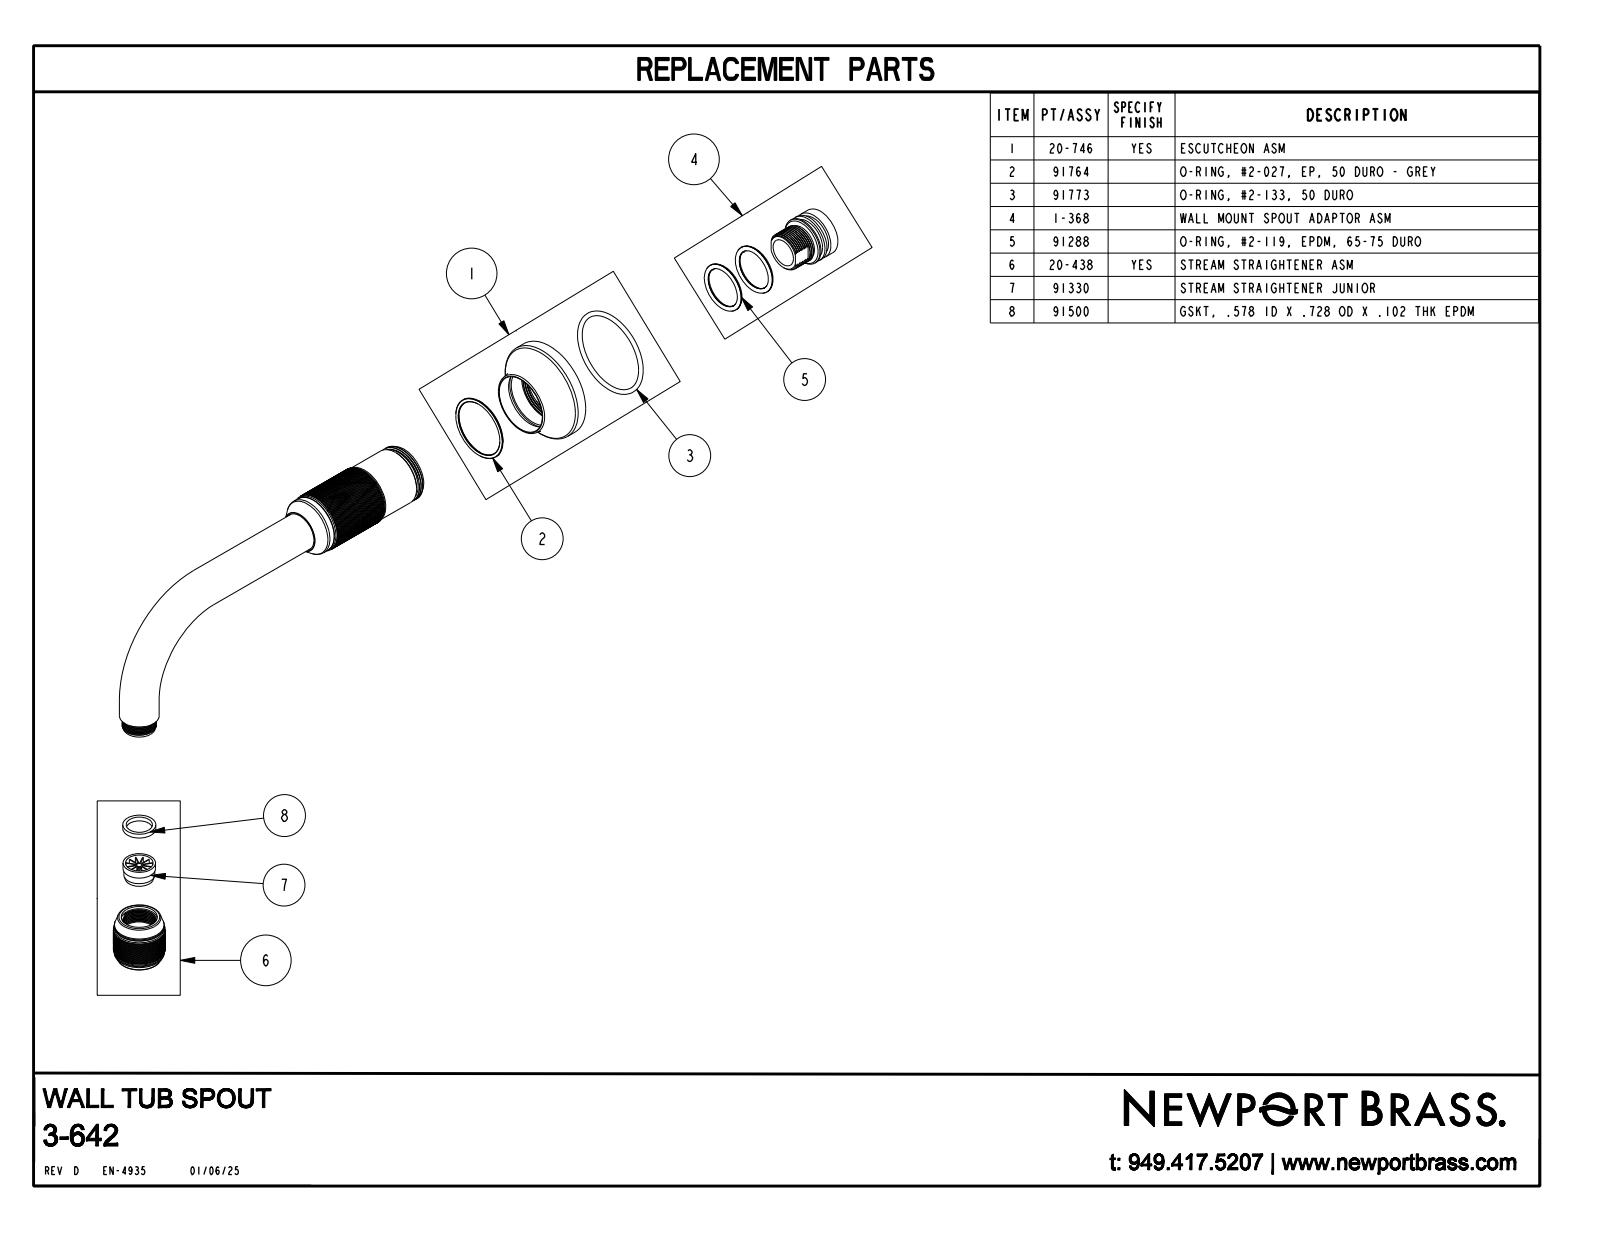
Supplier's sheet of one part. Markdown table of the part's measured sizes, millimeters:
| quantity | value |
| --- | --- |
| part name | 3-642 |
| STEP written by | CREO PARAMETRIC BY PTC INC, 2019352 (CONFIG_CONTROL_DESIGN) |
| units | millimeters |
| bodies | 1 solid, 14402 faces (7 planar, 2777 cylindrical, 11618 other) |
| overall size | 224 × 118.7 × 57.2 |
| volume | 173 500 mm³ |
| surface area | 32 080 mm² |
| round holes (diameter × count) | 17.6 × 1, 22.4 × 1 |
| round bosses / shafts (diameter × count) | 22.2 × 2, 57.2 × 1, 34.3 × 1, 33.3 × 1, 29 × 1, 27.9 × 1 |
| main face-to-face distances | 1.8, 22.9, 82.6, 59.7, 27.9, 26.2, 69.9, 47, 12.7 |
